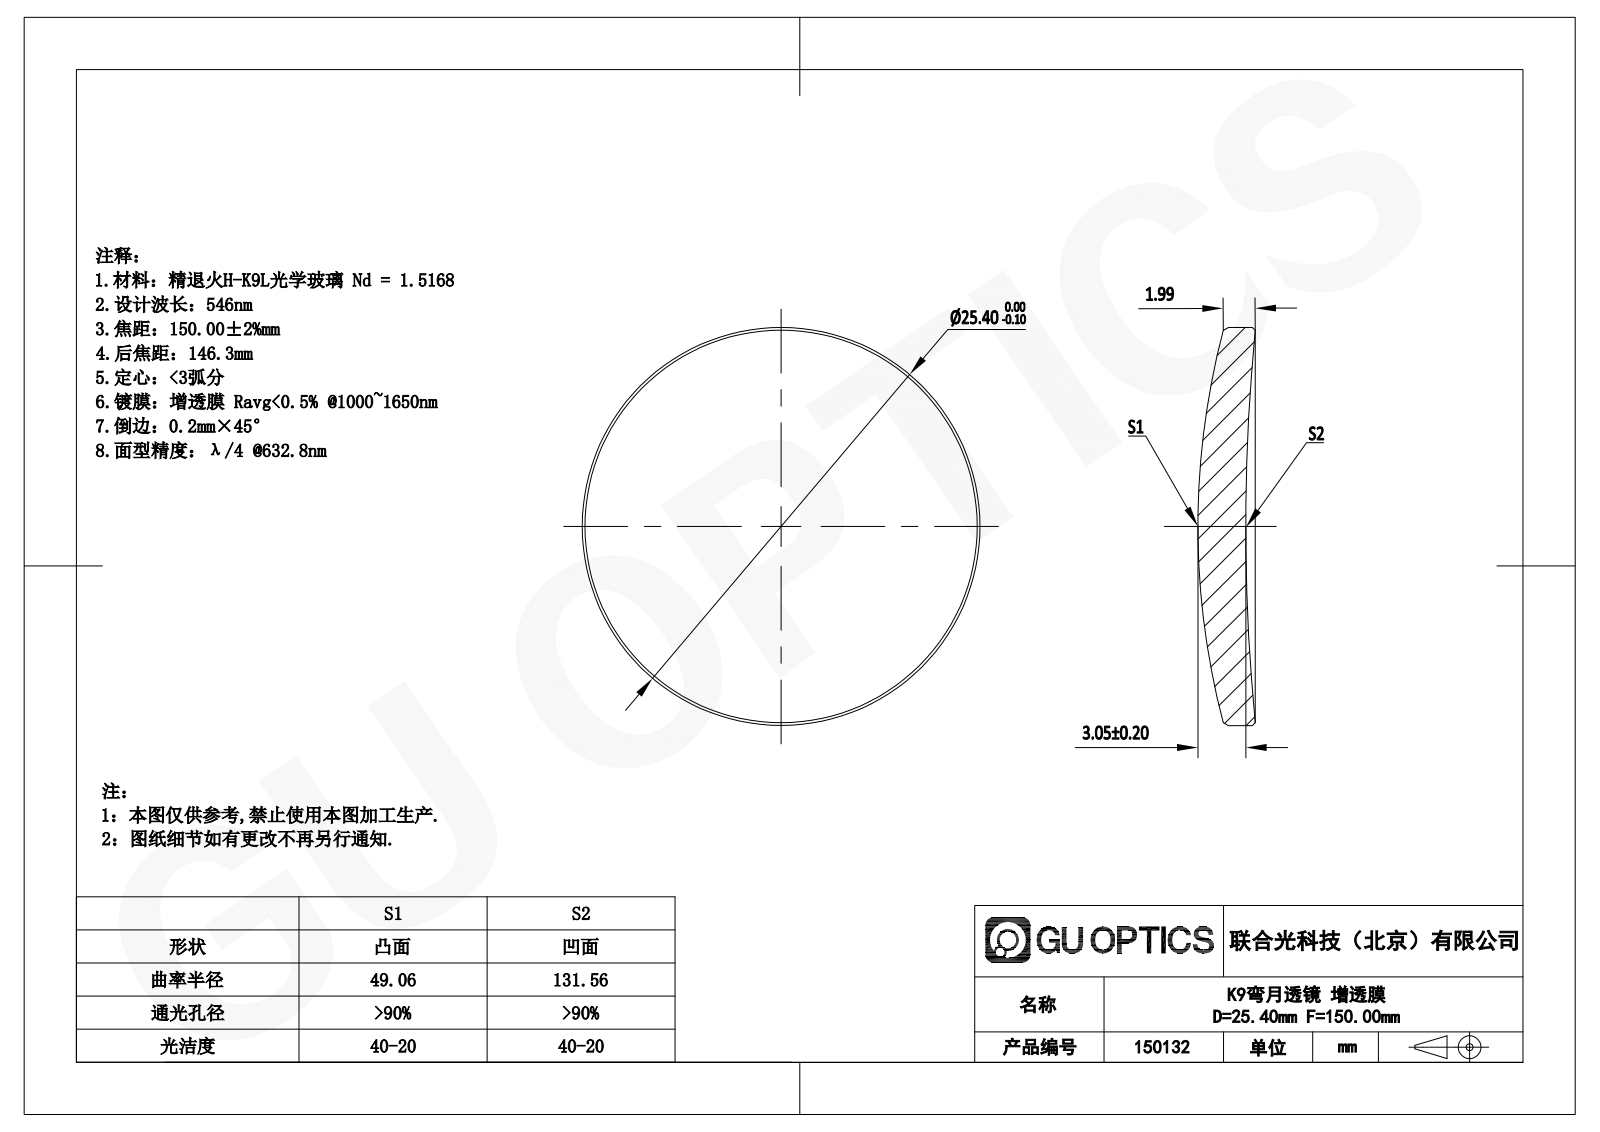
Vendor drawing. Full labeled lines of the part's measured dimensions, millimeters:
Part name (STEP PRODUCT): GLM1-025B-150-SWIR
STEP written by: SolidWorks 2022 (AUTOMOTIVE_DESIGN)
Units: millimetres
Bodies: 1 solid, 10 faces (0 planar, 2 cylindrical, 8 other)
Overall size (bounding box): 25.4 × 25.4 × 3.65
Volume: 1 280 mm³ · Surface area: 1 165 mm²
Round bosses / shafts (diameter × count): ⌀25.4 ×1
